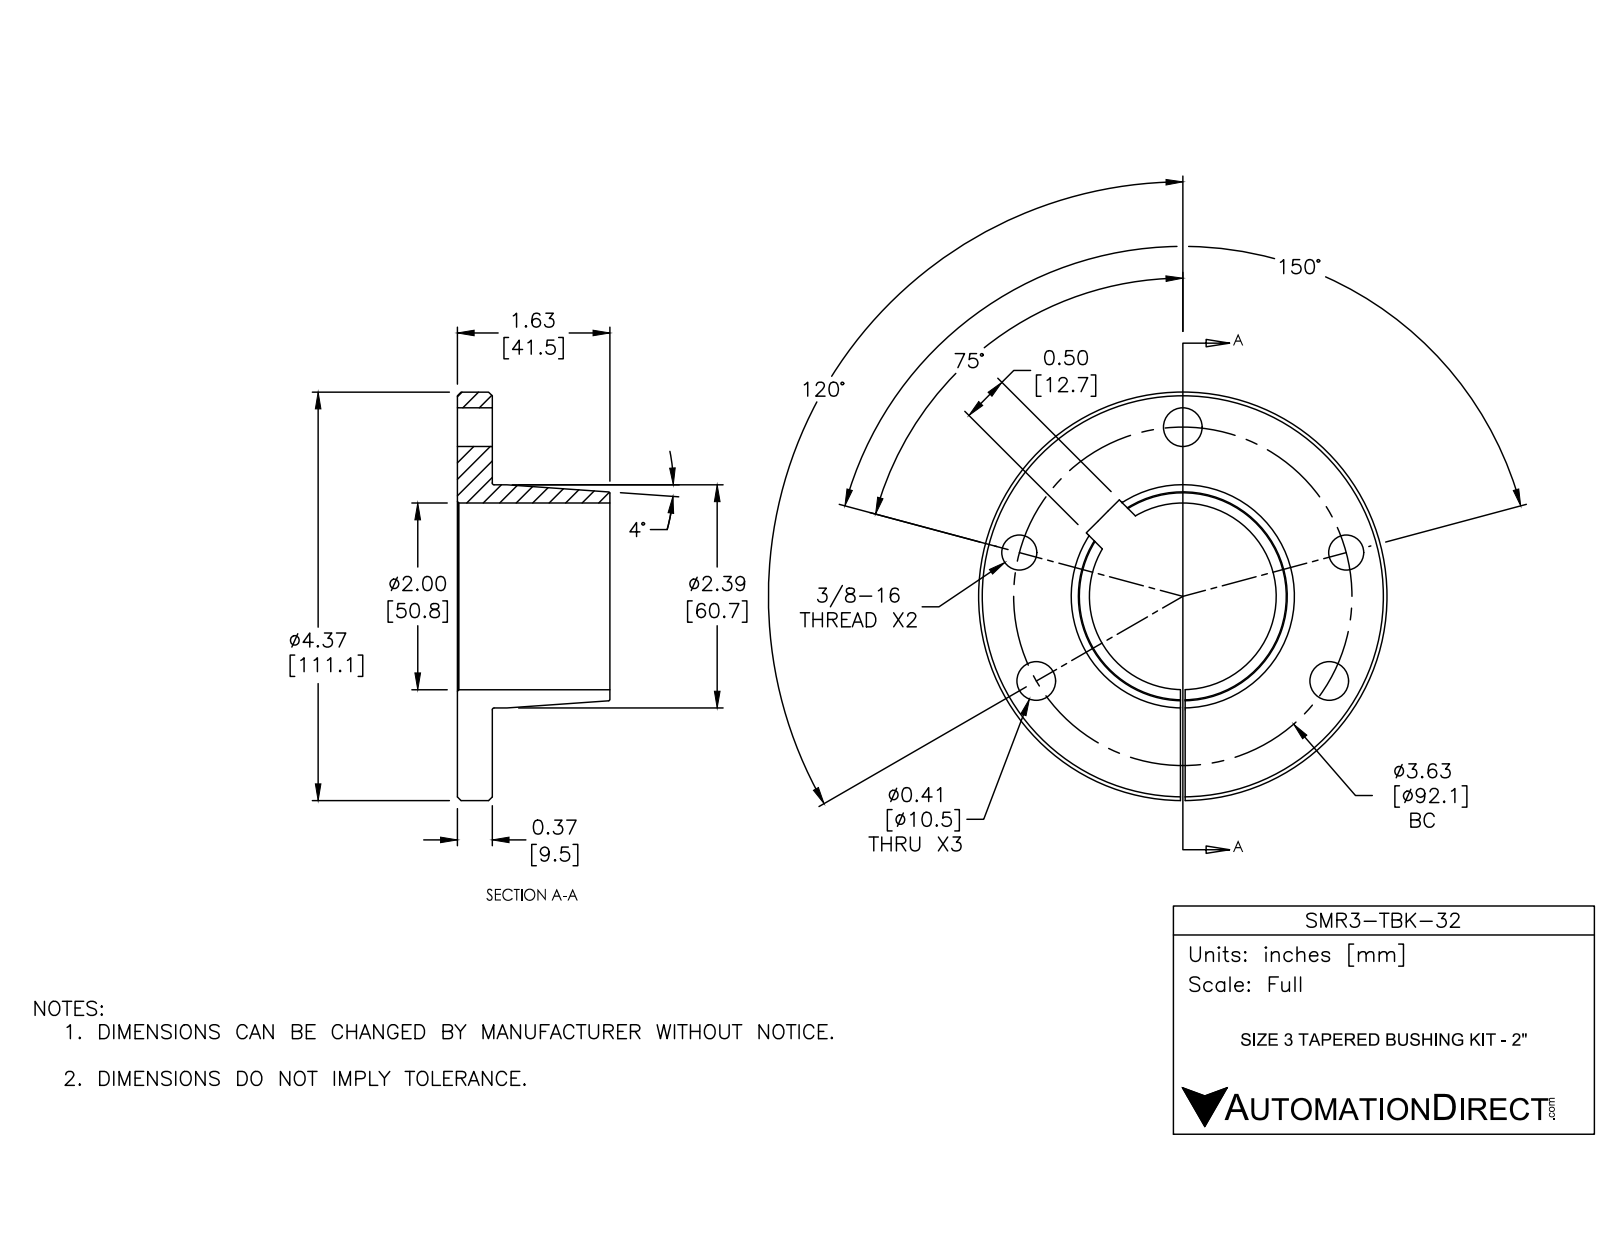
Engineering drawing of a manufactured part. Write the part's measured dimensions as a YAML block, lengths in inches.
part_name: "SMR3-TBK-32"
step_written_by: "SolidWorks 2016 (AUTOMOTIVE_DESIGN)"
units: inches
bodies: {solids: 1, faces: 99, planar: 11, cylindrical: 67, other: 21}
overall_size: [4.375, 4.375, 1.634]
volume: 5.391
surface_area: 48.6
round_holes:
  - {diameter: 0.413, count: 3}
  - {diameter: 0.315, count: 2}
  - {diameter: 0.375, count: 2}
  - {diameter: 2, count: 1}
  - {diameter: 2.016, count: 1}
round_bosses_or_shafts:
  - {diameter: 4.375, count: 1}
  - {diameter: 2.39, count: 1}
face_to_face_distances: [0.374, 0.051, 1.634, 1.26, 0.5]
hole_center_spacings: [1.813, 3.139, 1.387, 2.207, 3.594, 3.502]
